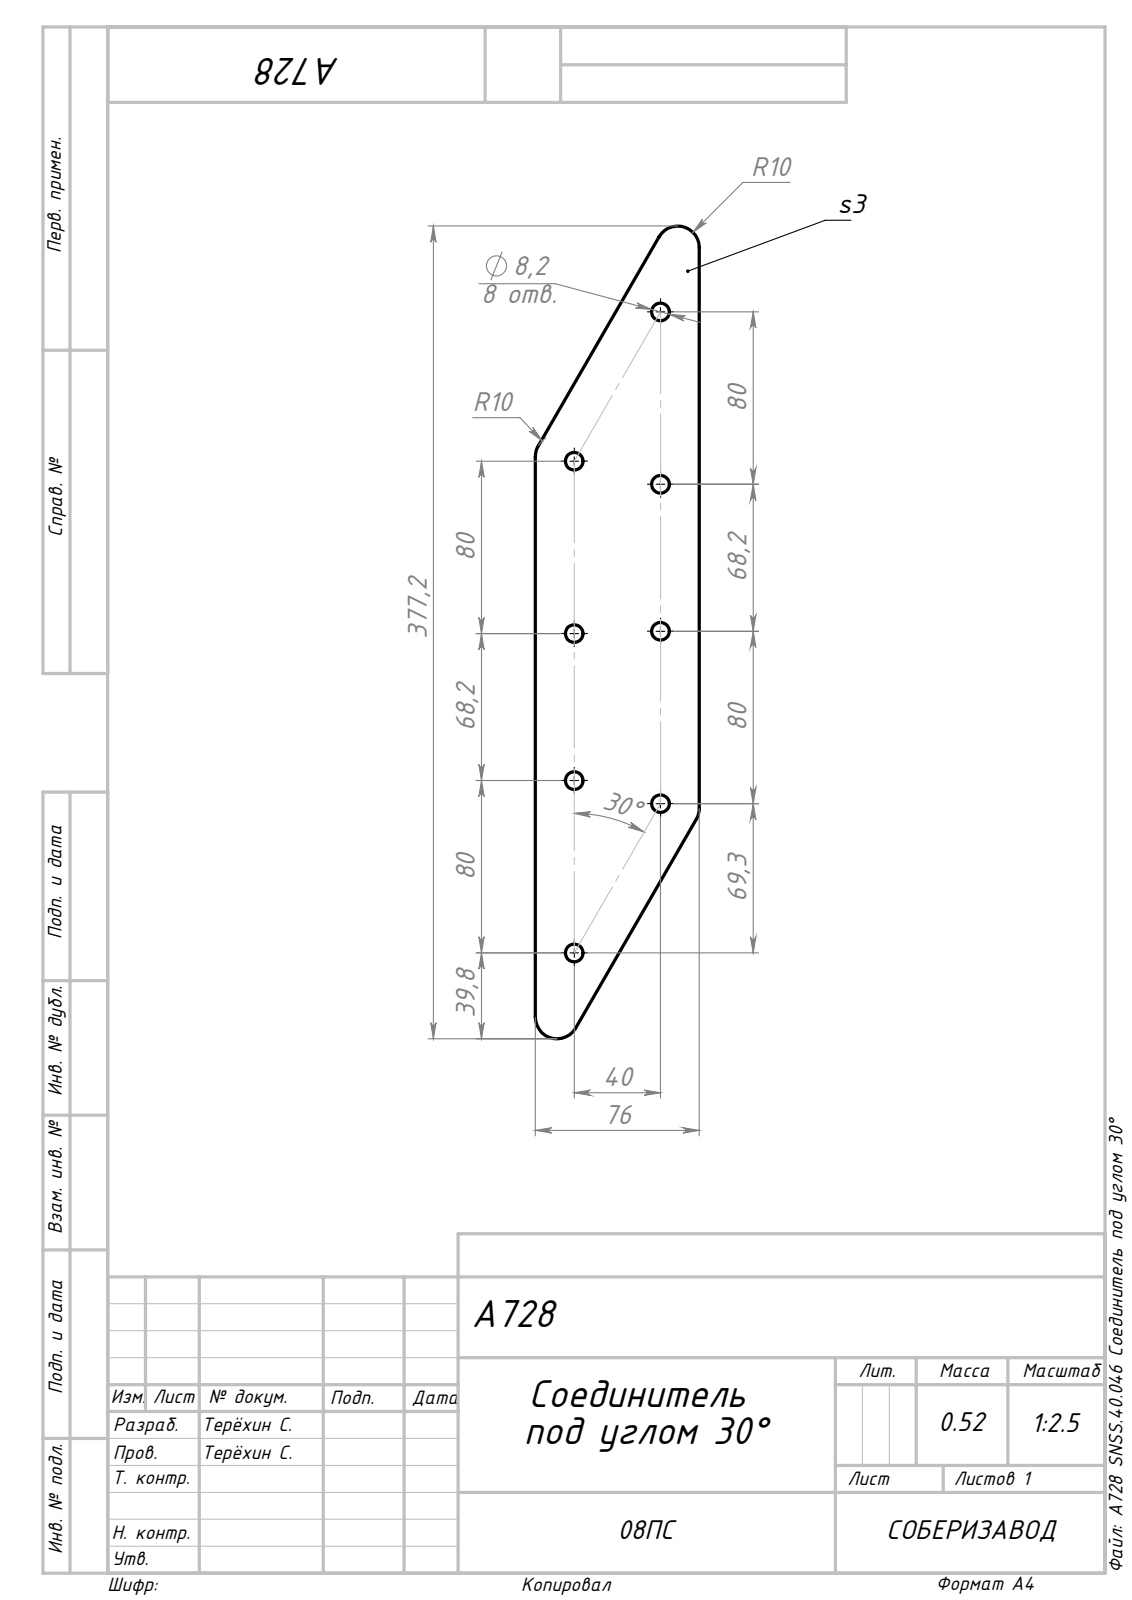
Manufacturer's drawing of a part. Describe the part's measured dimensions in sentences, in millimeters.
The part is named "A728 SNSS.40.046 Соединитель под углом 30°". Its 3-D file was written by "SolidWorks 2022 (AUTOMOTIVE_DESIGN)". It is 1 solid with 26 faces: 6 planar, 20 cylindrical and 0 other. Overall it measures 377.19 by 76 by 3 millimeters. Its volume is 65 720 cubic millimeters and its surface area 46 853 square millimeters. Round holes: 8 of diameter 8.2. Partial cylindrical surfaces (rounded edges, fillets, slot ends): 4 of radius 10. The main face-to-face distances are 3, 76, 150.11. The hole center spacings are 80, 148.2, 41.41, 68.2, 88.48, 154.55, 221.13, 228.2.
